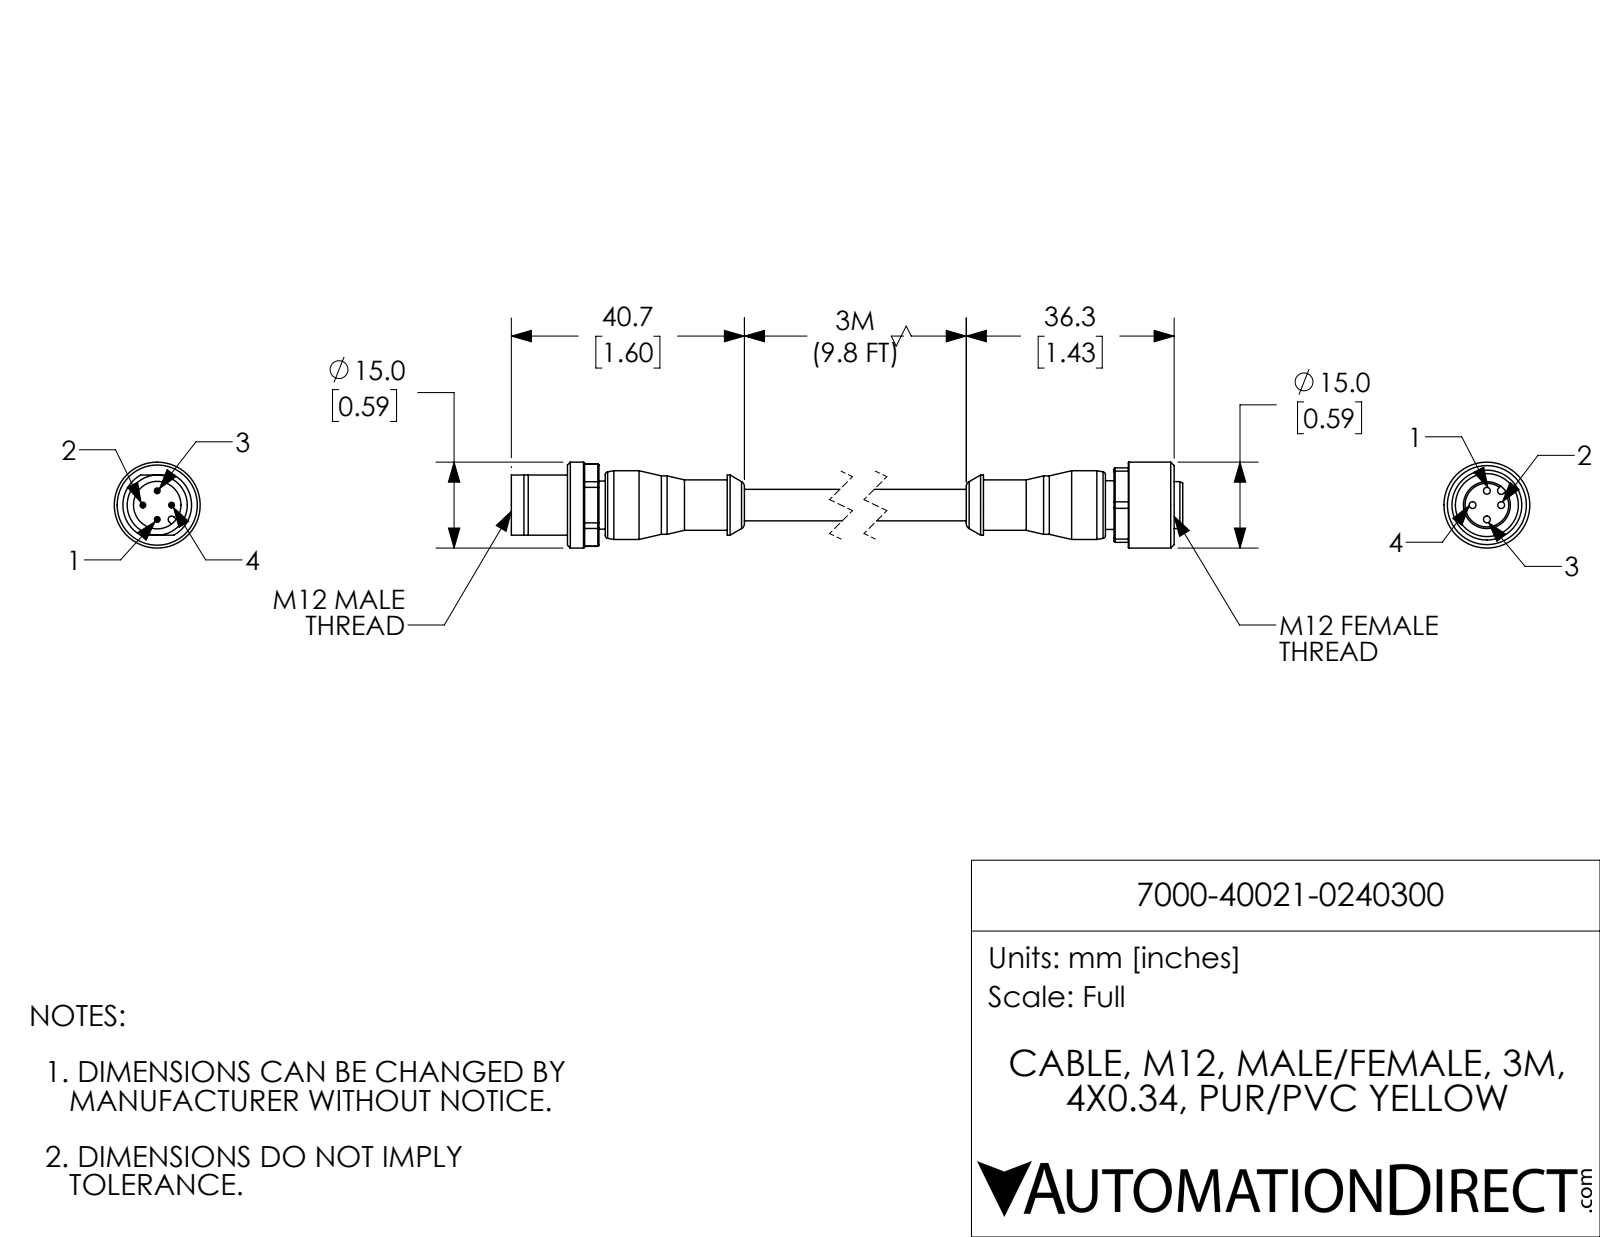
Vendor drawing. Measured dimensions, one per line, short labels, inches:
name: 7000-40021-0240300_MALE; 7000-40021-0240300_FEMALE; 7000-40021-0240300
written by: SolidWorks 2017 (AUTOMOTIVE_DESIGN)
unit: in
bodies: 2 solids, 188 faces (58 planar, 69 cylindrical, 61 other)
size: 5.138 × 0.591 × 0.591
volume: 0.488 in³; area: 7.93 in²
holes: 4× ⌀0.047, 1× ⌀0.327, 1× ⌀0.433
bosses: 4× ⌀0.039, 1× ⌀0.591, 1× ⌀0.472, 1× ⌀0.413, 1× ⌀0.402, 1× ⌀0.346, 1× ⌀0.335, 1× ⌀0.331
rounds: 1× R0.024, 1× R0.026, 1× R0.283
face distances: 0.472, 0.512, 0.118, 4.063, 0.413, 4.433, 2.217, 4.28, 0.295, 0.059
hole spacings: 0.098, 0.139, 0.197
